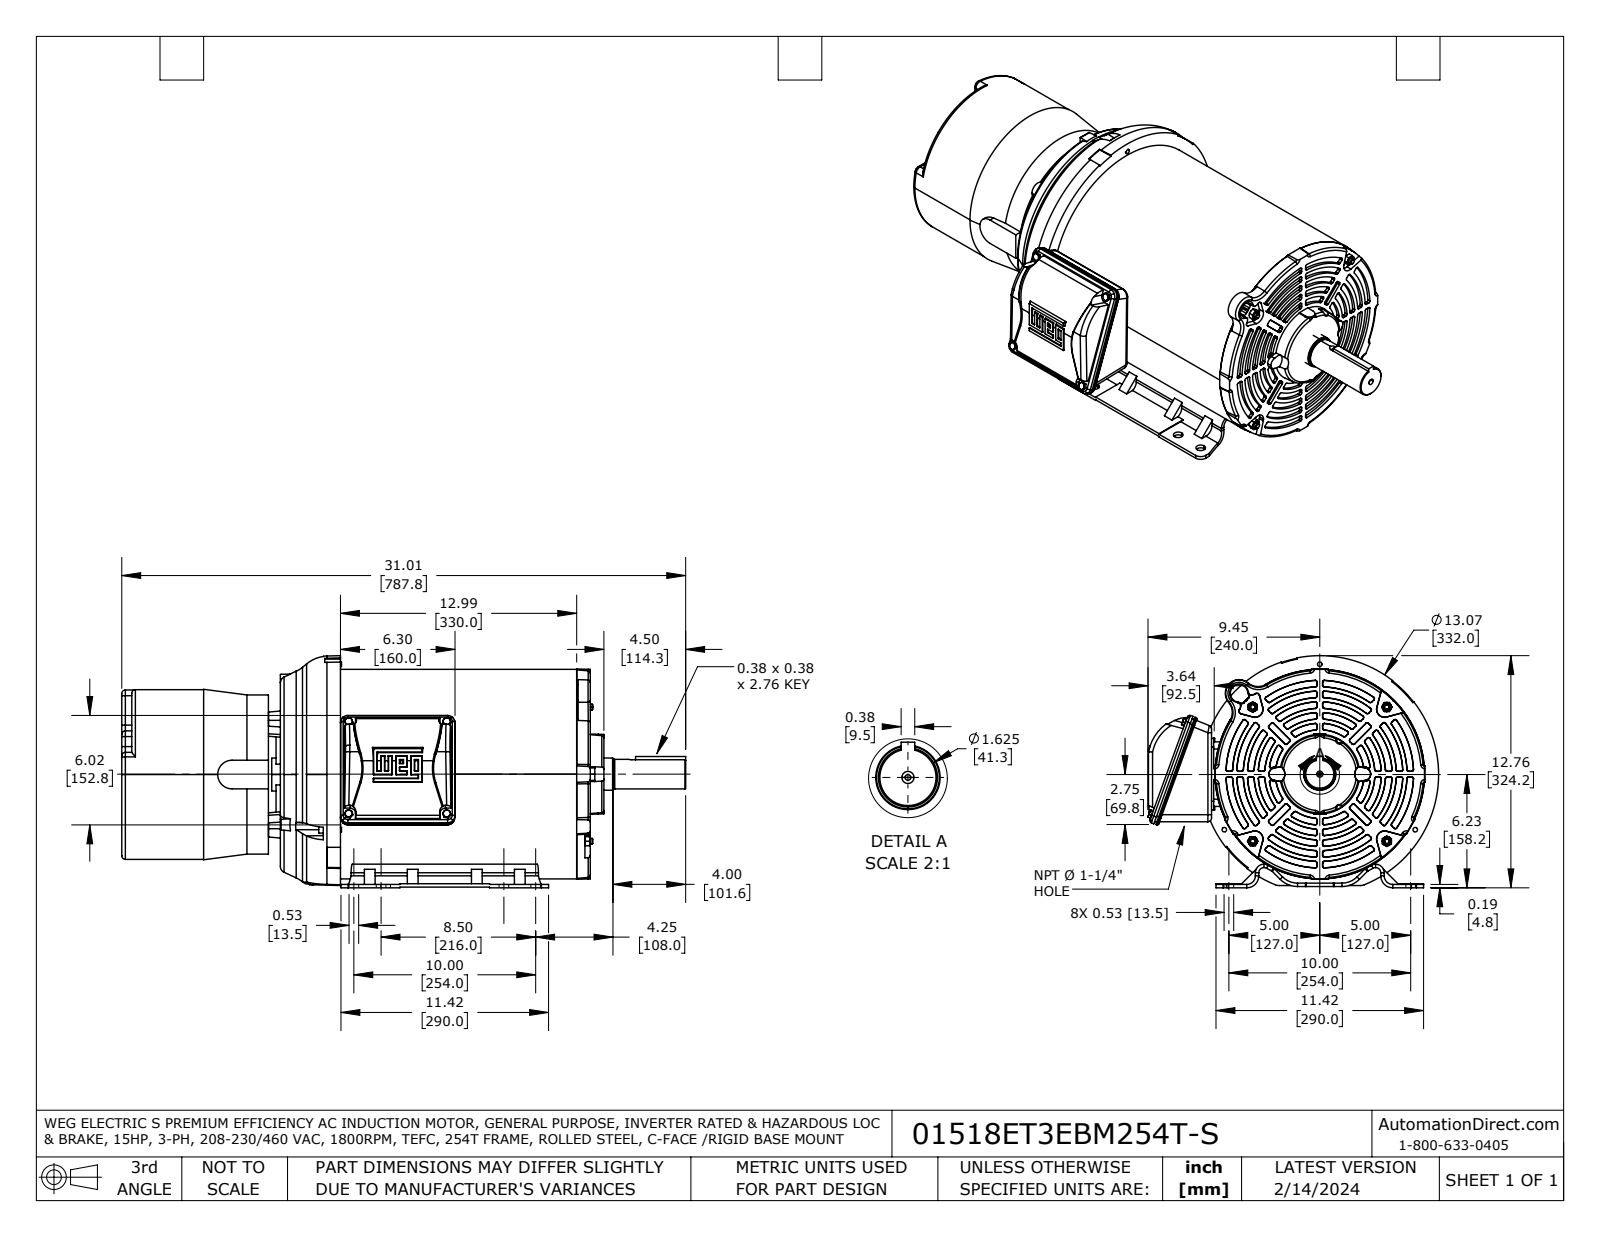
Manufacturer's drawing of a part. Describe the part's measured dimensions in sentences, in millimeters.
The part is named "01518ET3EBM254T-S". Its 3-D file was written by "SolidWorks 2021 (AUTOMOTIVE_DESIGN)". It is 24 solids with 1795 faces: 638 planar, 276 cylindrical and 881 other. Overall it measures 787.8 by 406 by 324.2 millimeters. Its volume is 40 670 000 cubic millimeters and its surface area 1 508 000 square millimeters. Round holes: 8 of diameter 10, 8 of diameter 13.5, 4 of diameter 6.5, 1 of diameter 4. Round bosses or shafts: 4 of diameter 8.9, 4 of diameter 8, 3 of diameter 9.5, 3 of diameter 6.4, 1 of diameter 292.6, 1 of diameter 237, 1 of diameter 222.3, 1 of diameter 215.9. Partial cylindrical surfaces (rounded edges, fillets, slot ends): 42 of radius 0.5, 22 of radius 8, 12 of radius 10, 7 of radius 5, 6 of radius 2, 4 of radius 3.5, 4 of radius 5.2, 4 of radius 10.1. The main face-to-face distances are 330, 4.7, 105.5, 435.5, 19, 200, 305.5, 635.5, 654.5, 454.5. The hole center spacings are 209.6, 254, 44.4, 60, 132.5, 149.6, 187.4, 257.9.
